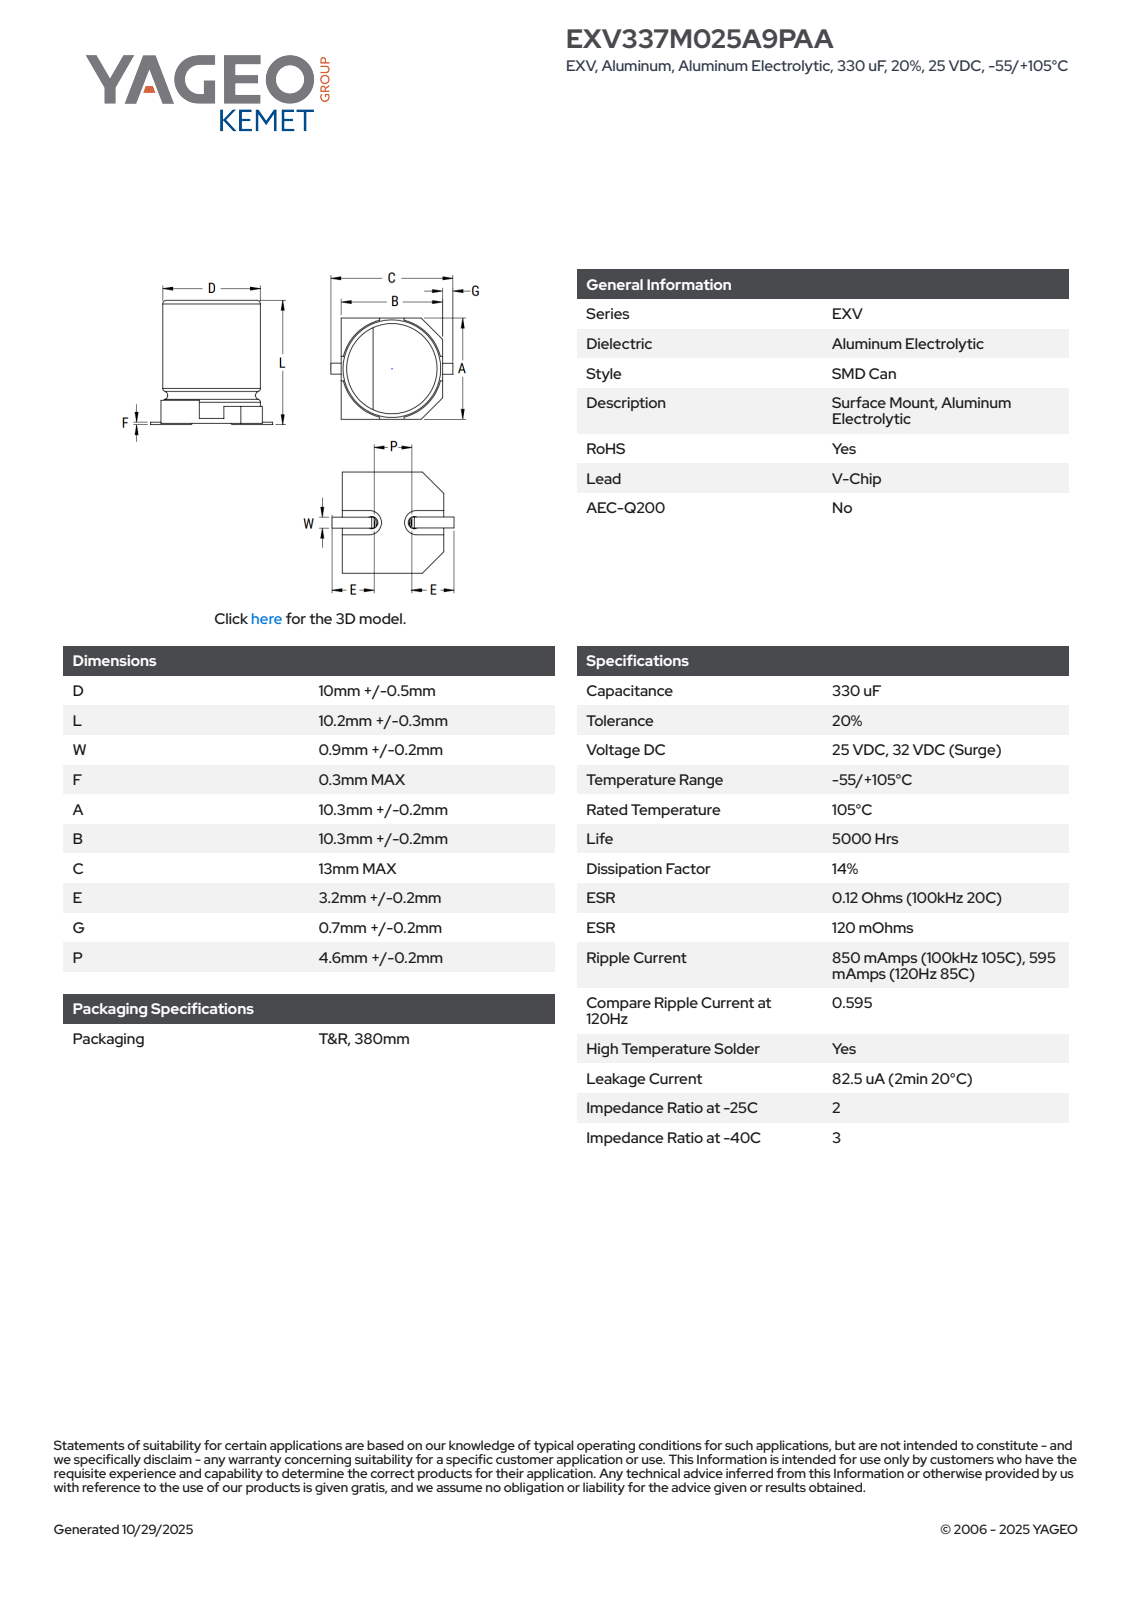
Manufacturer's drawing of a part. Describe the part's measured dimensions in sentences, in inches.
The part is named "CAC_S_10X10.2_D10.5L10.5W1.1F0.3A10.5B10.5C13E3.7P4.8". Its 3-D file was written by "SolidWorks 2014 (AUTOMOTIVE_DESIGN)". It is 5 solids with 78 faces: 61 planar, 11 cylindrical and 6 other. Overall it measures 0.48 by 0.414 by 0.413 inches. Its volume is 0.051 cubic inches and its surface area 1.23 square inches. Round bosses or shafts: 1 of diameter 0.395. Partial cylindrical surfaces (rounded edges, fillets, slot ends): 2 of radius 0.008, 1 of radius 0.164, 1 of radius 0.207. The main face-to-face distances are 0.02, 0.402, 0.381, 0.413, 0.103, 0.083, 0.298, 0.032, 0.115, 0.069.
